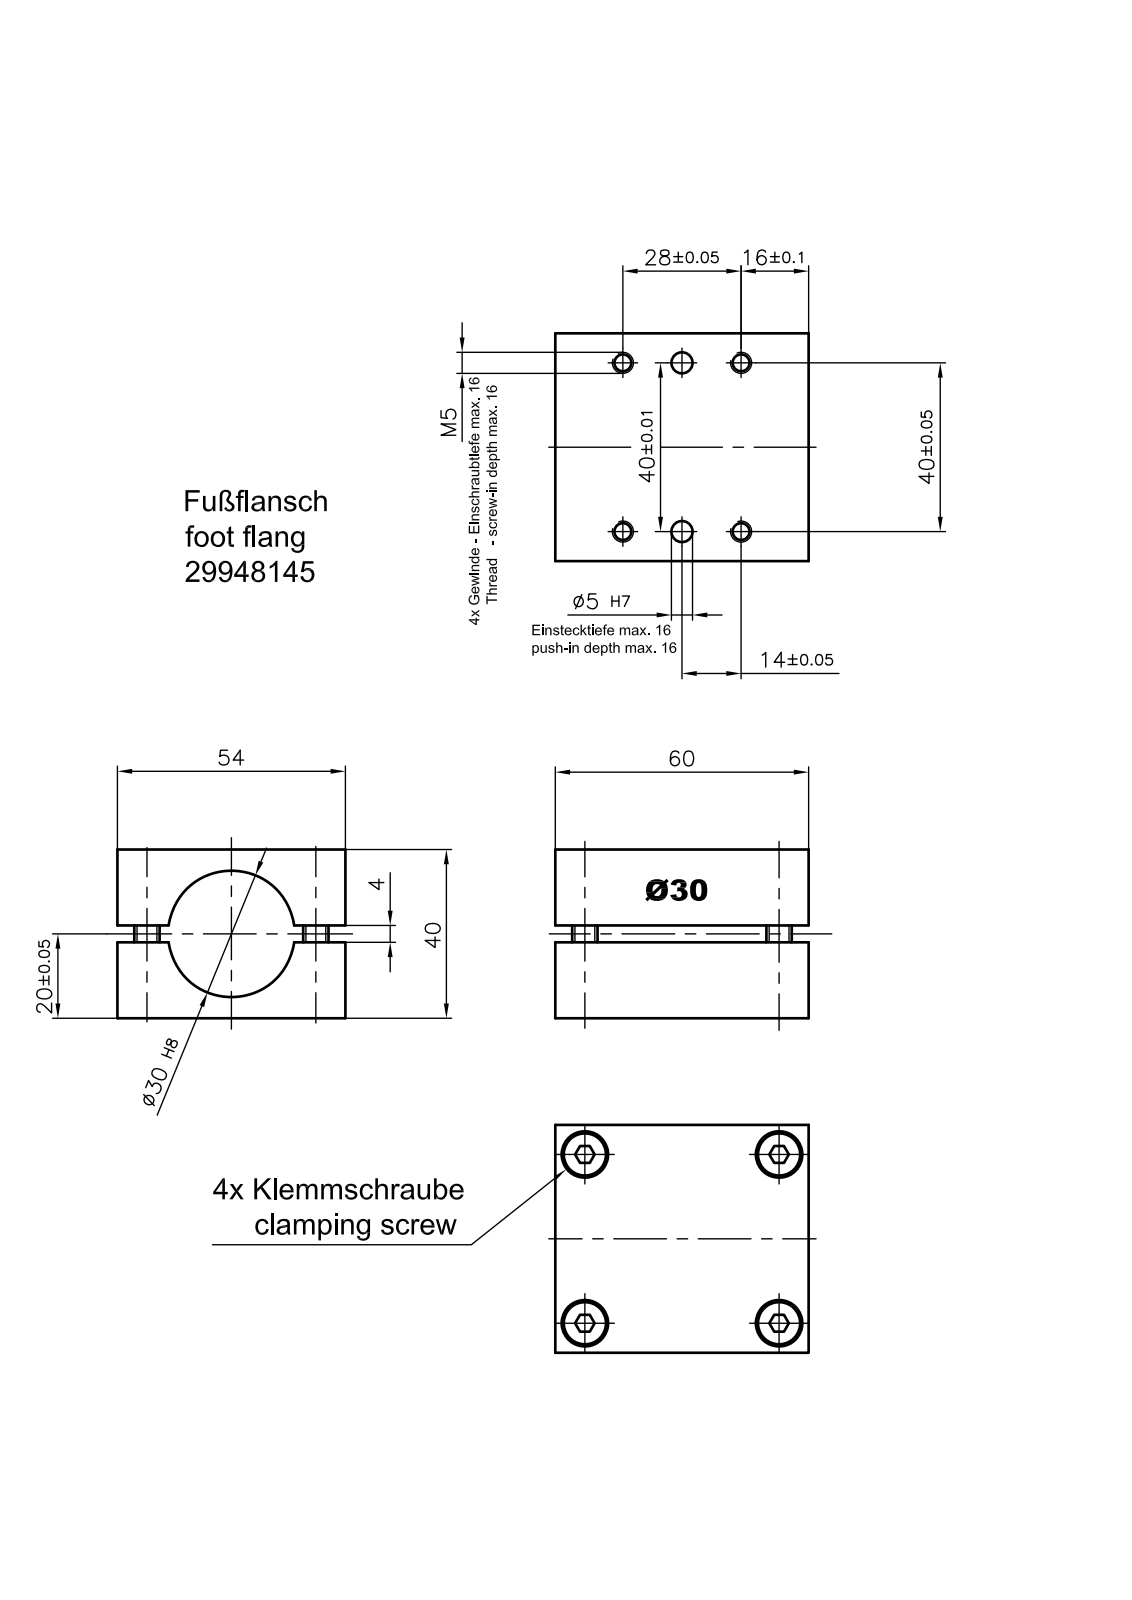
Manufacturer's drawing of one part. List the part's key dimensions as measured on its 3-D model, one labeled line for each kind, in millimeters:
Part name (STEP PRODUCT): 29948145 \S\X30 Fu\S\_flansch
STEP written by: Autodesk Inventor 2008 (AUTOMOTIVE_DESIGN)
Units: millimetres
Bodies: 1 solid, 94 faces (50 planar, 10 cylindrical, 34 other)
Overall size (bounding box): 60 × 54 × 40
Volume: 78 877 mm³ · Surface area: 26 924 mm²
Round holes (diameter × count): ⌀30 ×1
Round bosses / shafts (diameter × count): ⌀10 ×4, ⌀6 ×4
Main face-to-face distances: 40, 18, 22, 54, 60, 4, 5, 14, 36, 34
